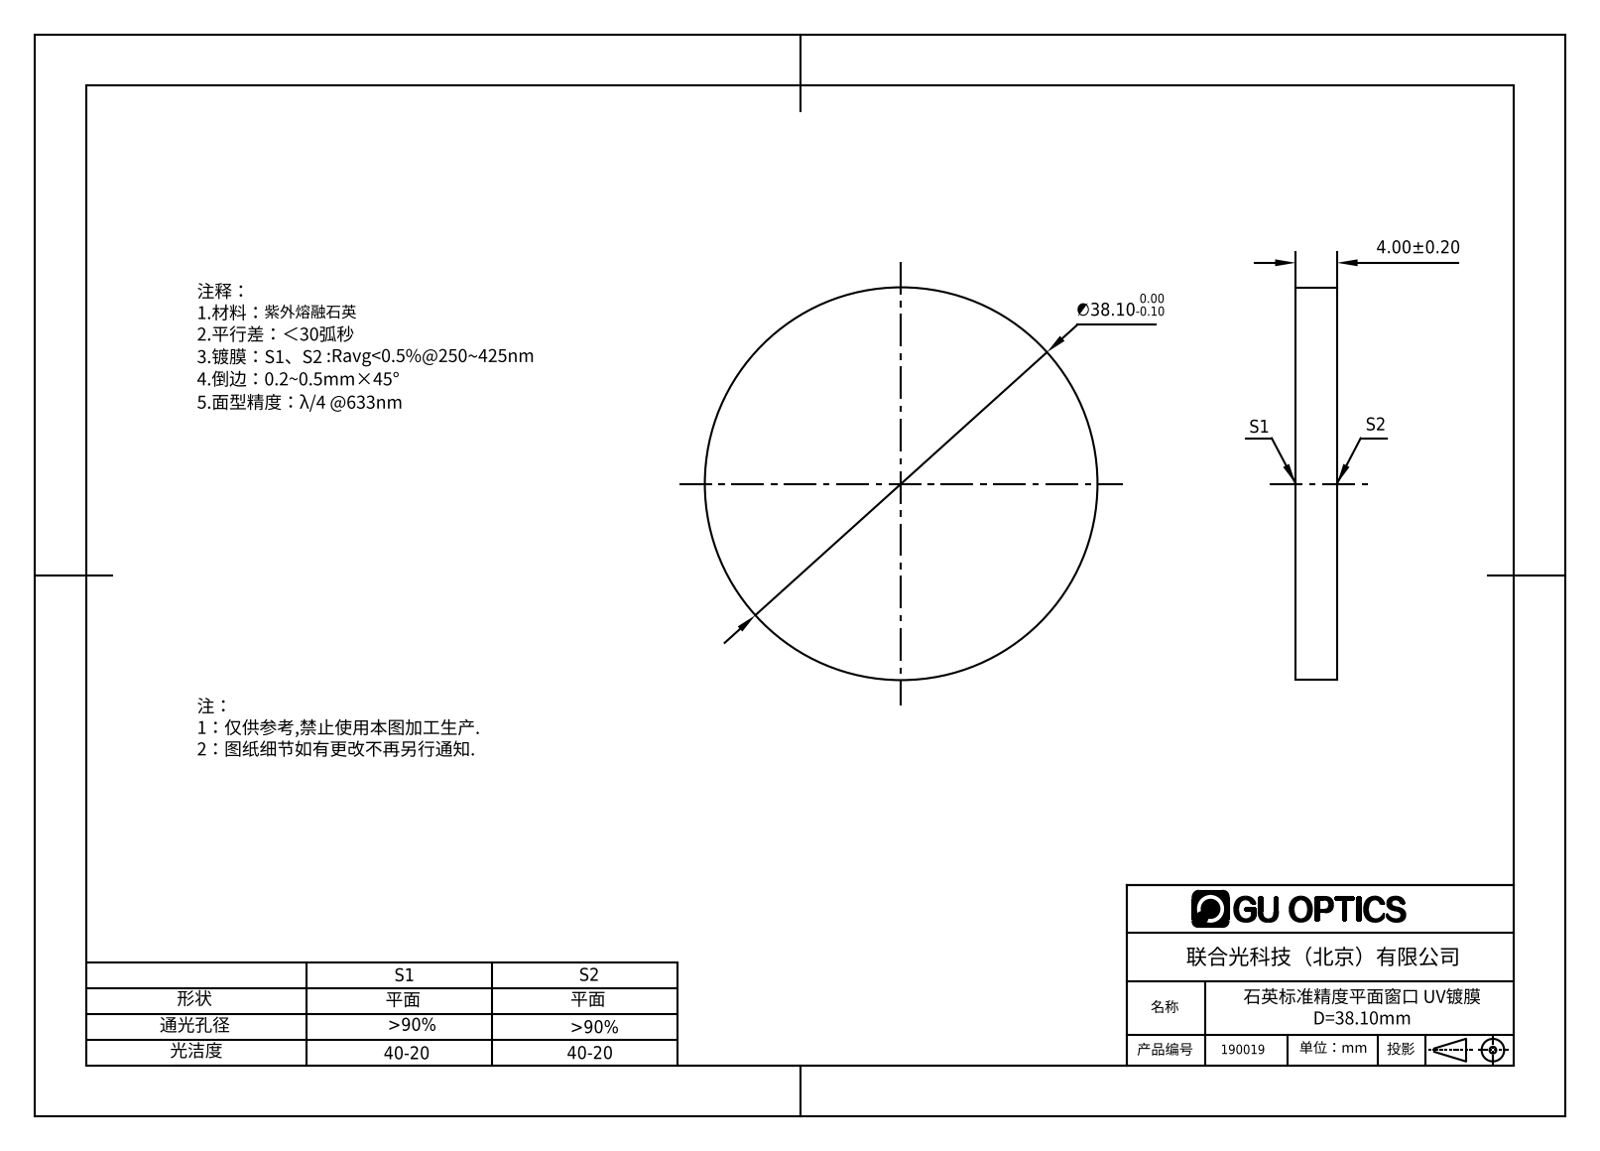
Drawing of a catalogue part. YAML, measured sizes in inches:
part_name: "180008"
step_written_by: "SolidWorks 2016 (AUTOMOTIVE_DESIGN)"
units: inches
bodies: {solids: 1, faces: 4, planar: 2, cylindrical: 2, other: 0}
overall_size: [1.5, 1.5, 0.157]
volume: 0.278
surface_area: 4.276
round_bosses_or_shafts:
  - {diameter: 1.5, count: 1}
face_to_face_distances: [0.157]
